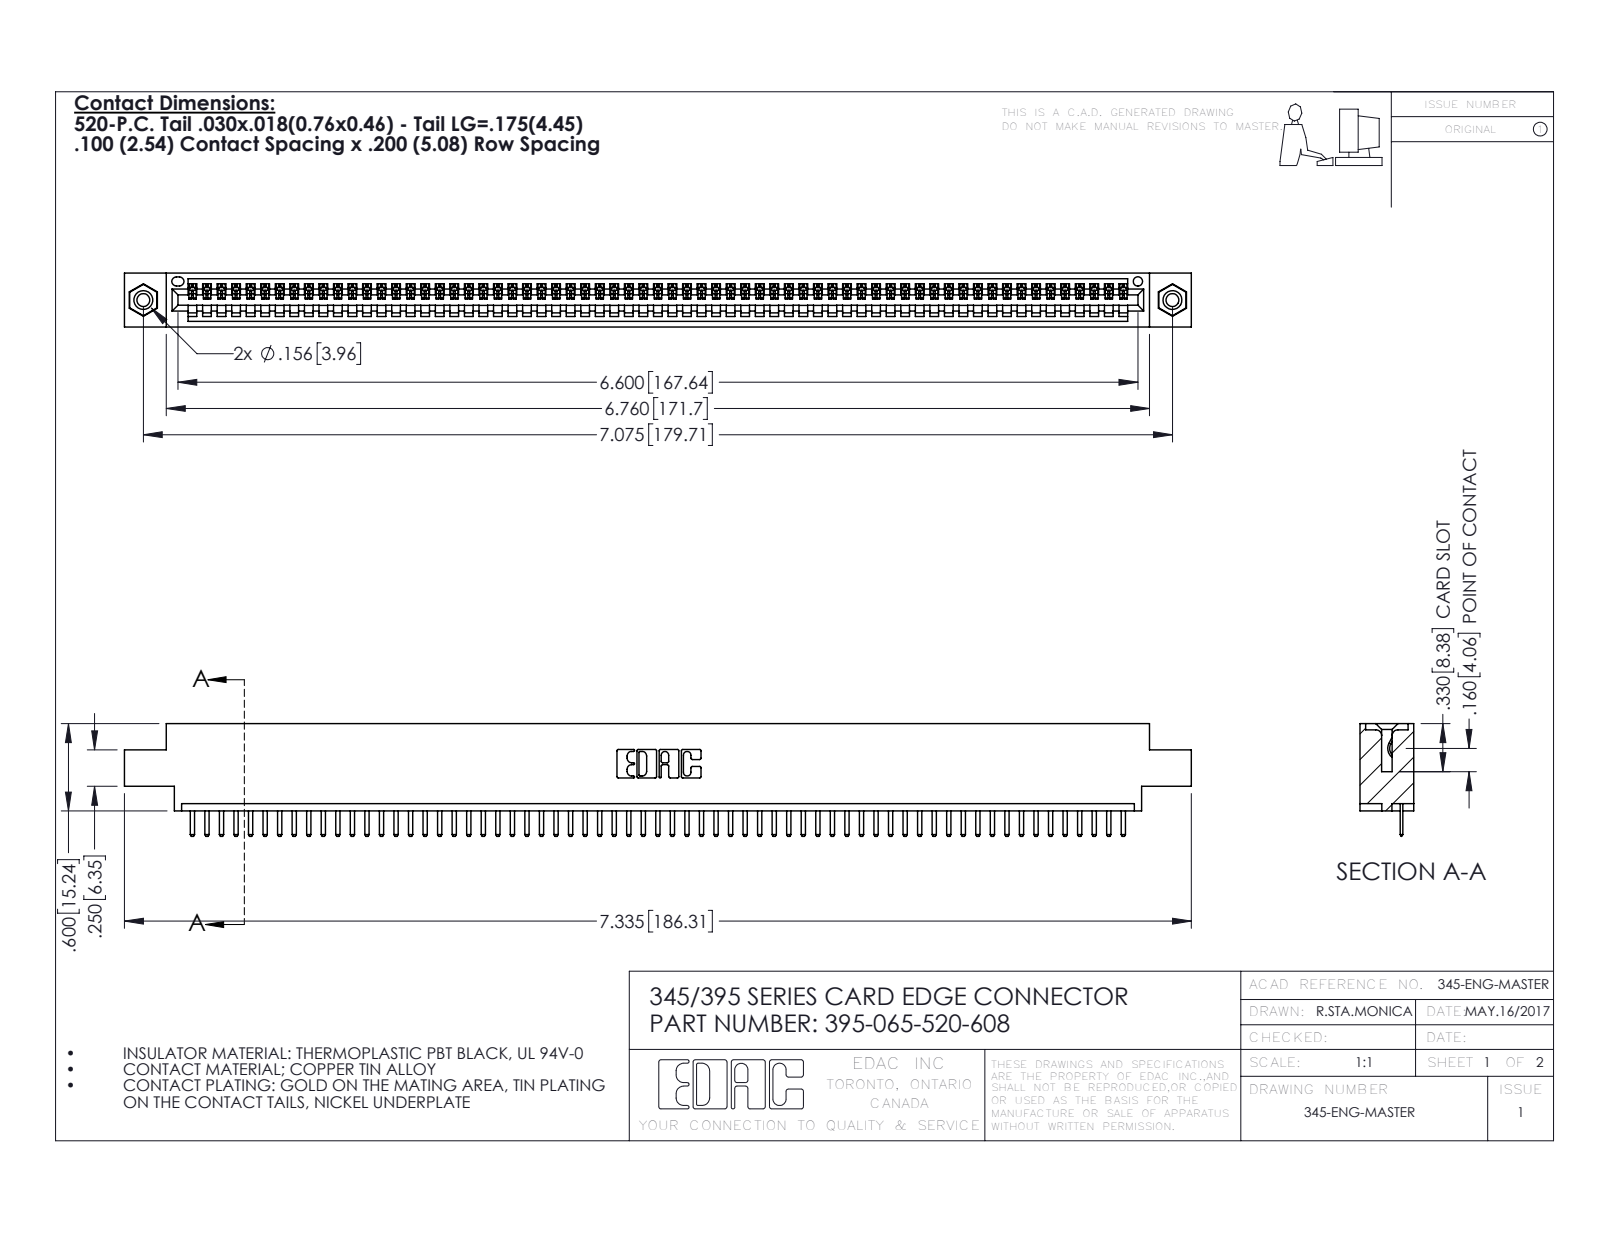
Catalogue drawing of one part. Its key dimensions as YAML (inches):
part_name: "345 Part_0.170 Offset - 0.156 Dia-TI; 395-065-520-608; 345-292-001_345-293-120; 345-250-001_345-250-003-102"
step_written_by: "SolidWorks 2016 (CONFIG_CONTROL_DESIGN)"
units: inches
bodies: {solids: 68, faces: 4220, planar: 2846, cylindrical: 1358, other: 16}
overall_size: [7.335, 0.775, 0.37]
volume: 1.073
surface_area: 35.97
round_holes:
  - {diameter: 0.089, count: 2}
  - {diameter: 0.125, count: 2}
  - {diameter: 0.156, count: 2}
  - {diameter: 0.064, count: 1}
round_bosses_or_shafts:
  - {diameter: 0.155, count: 2}
partial_cylinders:
  - {radius: 0.01, count: 132}
  - {radius: 0.006, count: 130}
  - {radius: 0.01, count: 22}
  - {radius: 0.007, count: 6}
  - {radius: 0.031, count: 6}
  - {radius: 0.026, count: 3}
  - {radius: 0.031, count: 2}
  - {radius: 0.04, count: 2}
face_to_face_distances: [0.072, 0.298, 0.37, 0.2, 0.098, 0.272, 0.025, 0.225, 0.072, 0.175]
hole_center_spacings: [0.27, 6.839, 7.075]
